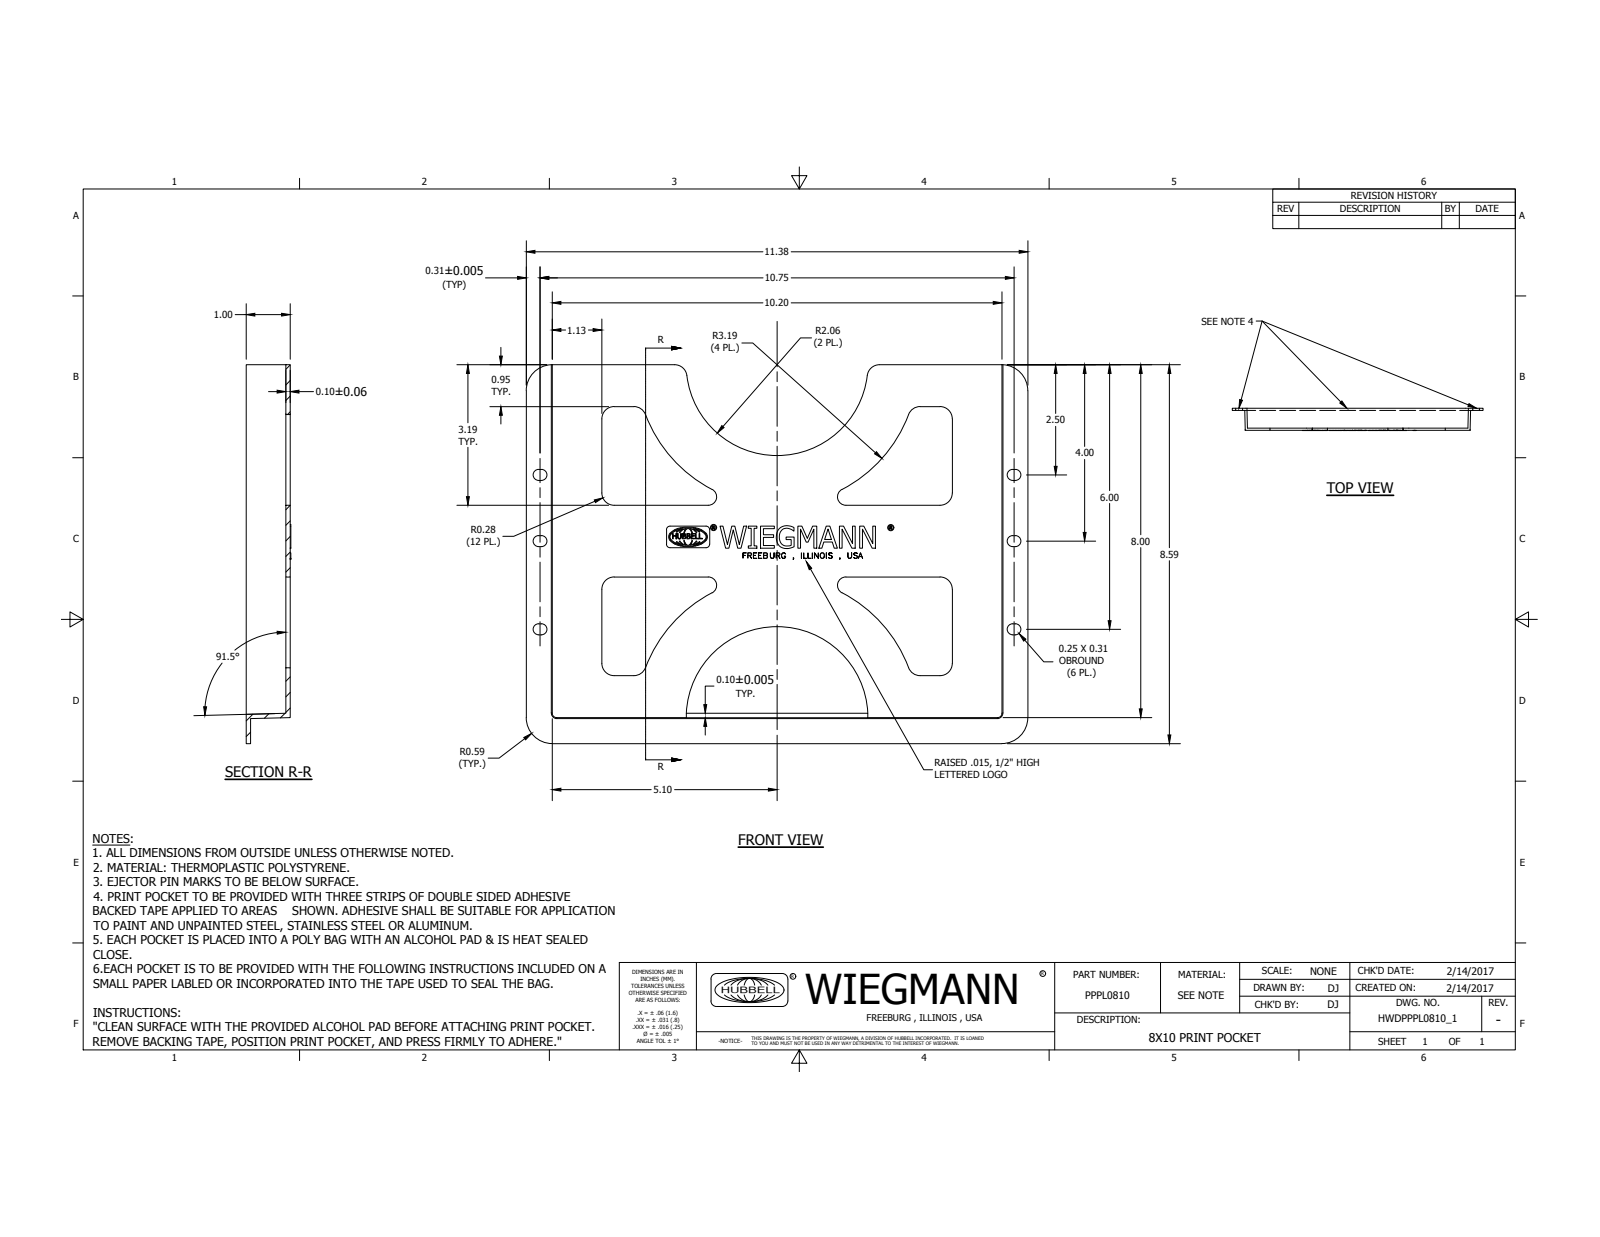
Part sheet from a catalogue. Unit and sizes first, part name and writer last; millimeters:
Units: millimetres
Overall size (bounding box): 288.93 × 218.19 × 25.73
Round holes (diameter × count): ⌀2.85 ×2
Round bosses / shafts (diameter × count): ⌀3.61 ×2
Partial cylindrical surfaces — rounded edges, fillets, slot ends (radius × count): R7.11 ×14, R3.17 ×12, R2.07 ×4, R3.49 ×4, R3.87 ×4, R4.83 ×4, R4.93 ×4, R5.31 ×4
Main face-to-face distances: 2.54, 22.86, 25.4, 20.32, 25.73, 23.19, 2.87, 0.33, 288.92, 218.19
Hole centre spacings: 102.15
Volume: 150 833 mm³ · Surface area: 124 598 mm²
Bodies: 1 solid, 887 faces (679 planar, 142 cylindrical, 66 other)
Part name (STEP PRODUCT): PPPL0810
STEP written by: Autodesk Inventor 2016 (AUTOMOTIVE_DESIGN)
